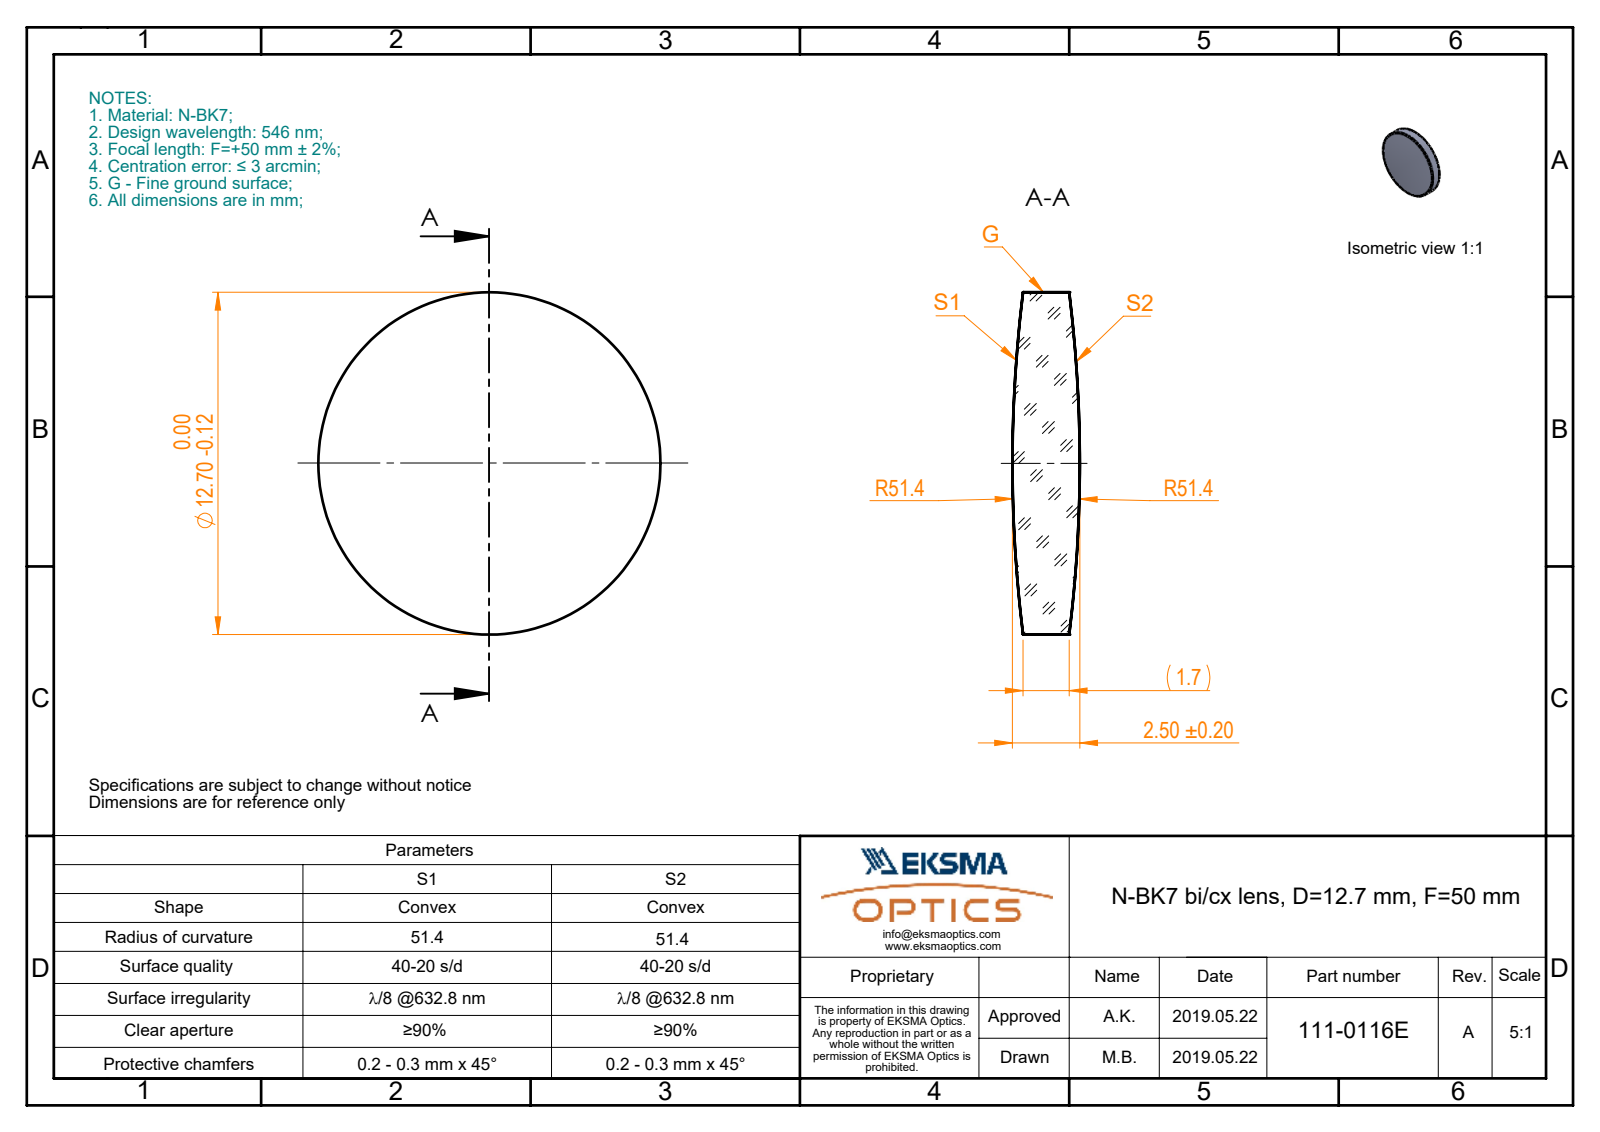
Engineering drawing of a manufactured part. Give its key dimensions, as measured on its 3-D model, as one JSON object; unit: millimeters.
{"part_name": "111-0116E BK7 bi-cx 12.7 F50", "step_written_by": "SolidWorks 2017 (CONFIG_CONTROL_DESIGN)", "units": "millimeters", "bodies": {"solids": 1, "faces": 6, "planar": 0, "cylindrical": 2, "other": 4}, "overall_size": [12.7, 12.7, 2.5], "volume_mm3": 267, "surface_area_mm2": 323, "round_bosses_or_shafts": [[12.7, 1]]}
